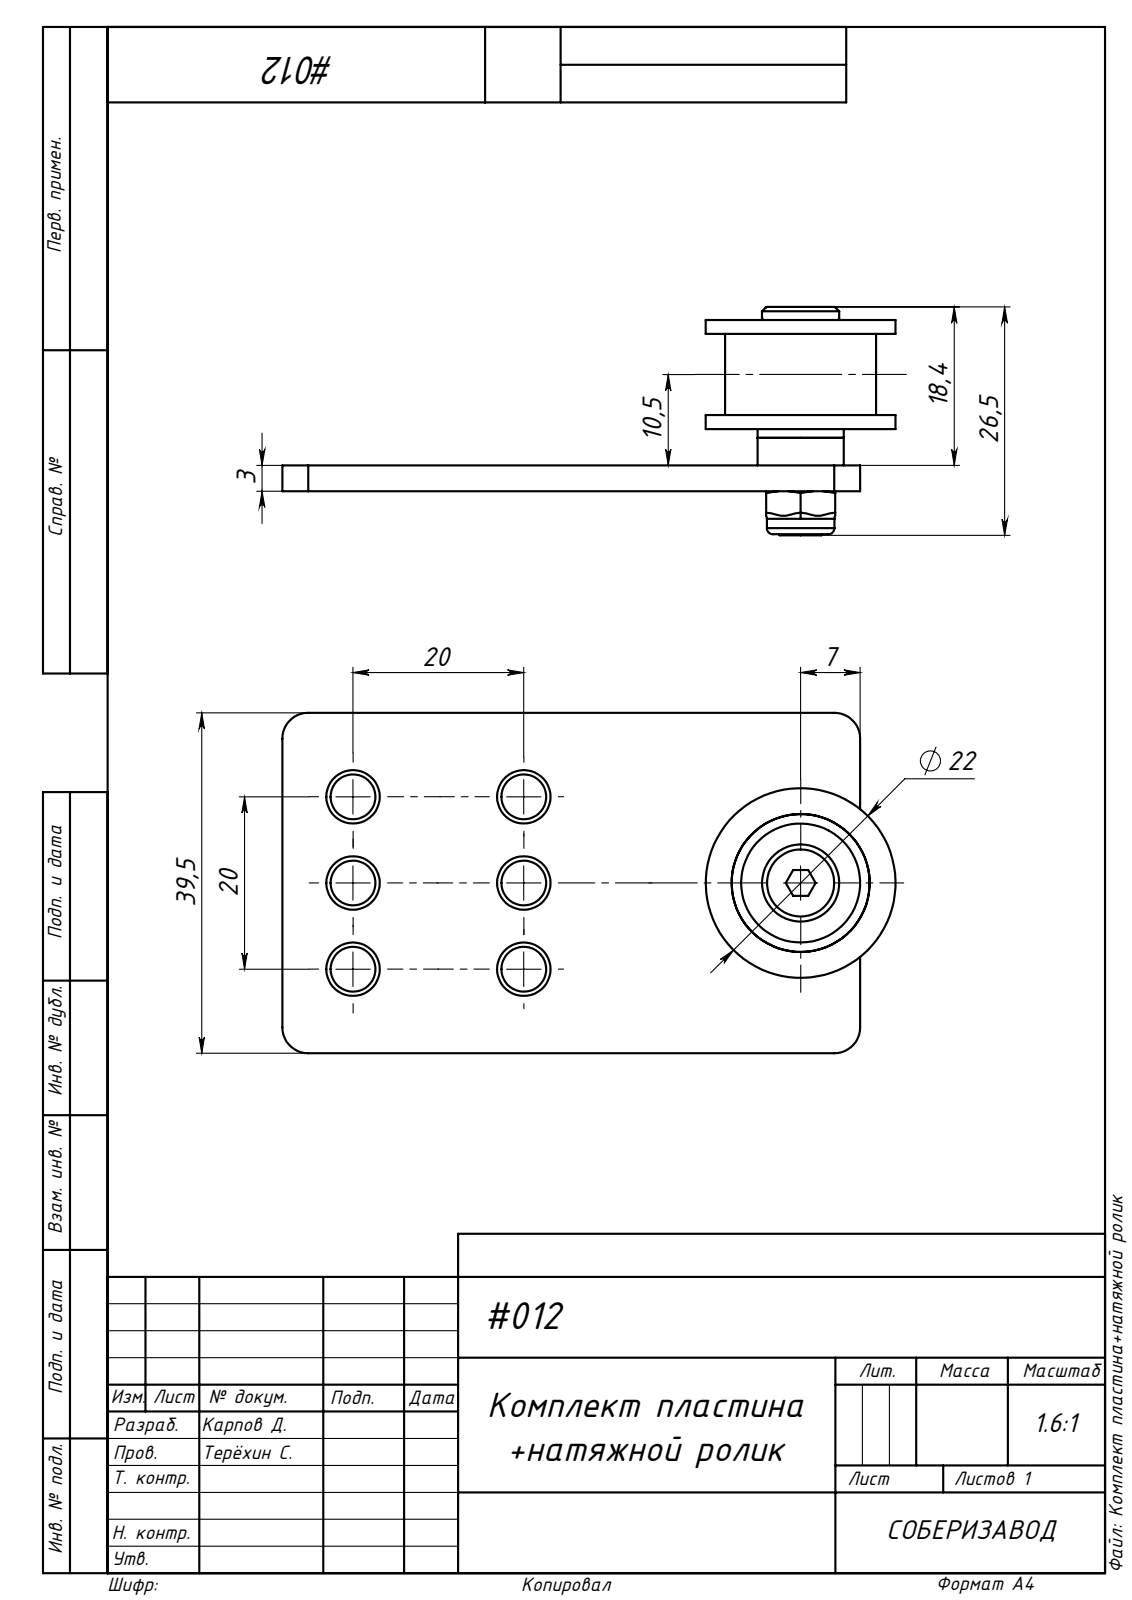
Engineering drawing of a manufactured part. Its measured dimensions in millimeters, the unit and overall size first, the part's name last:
Units: millimetres
Overall size (bounding box): 71.1 × 39.5 × 26.5
Round holes (diameter × count): ⌀5.2 ×7, ⌀4.13 ×1, ⌀5 ×1, ⌀5.25 ×1, ⌀13.8 ×1, ⌀14 ×1, ⌀16 ×1
Round bosses / shafts (diameter × count): ⌀22 ×1, ⌀17.5 ×1, ⌀10 ×1, ⌀8.95 ×1, ⌀8.6 ×1, ⌀7.83 ×1
Partial cylindrical surfaces — rounded edges, fillets, slot ends (radius × count): R3 ×4
Main face-to-face distances: 3, 7.67, 4.65, 3.02, 0.35, 3.37, 7.2, 4.2, 19.87, 16.87
Hole centre spacings: 10, 22.18, 19.8, 20, 28.14, 33.62, 52.85, 32.1
Volume: 11 394 mm³ · Surface area: 10 977 mm²
Bodies: 9 solids, 174 faces (48 planar, 74 cylindrical, 52 other)
Part name (STEP PRODUCT): A200 Дистанционная втулка 5х1 8_00; A229 Самоконтрящаяся гайка M5_00; A211 Высокоточная дистанционная шайба 5 мм_00; Комплект пластина+натяжной ролик (+2 more)
STEP written by: SolidWorks 2020 (AUTOMOTIVE_DESIGN)
